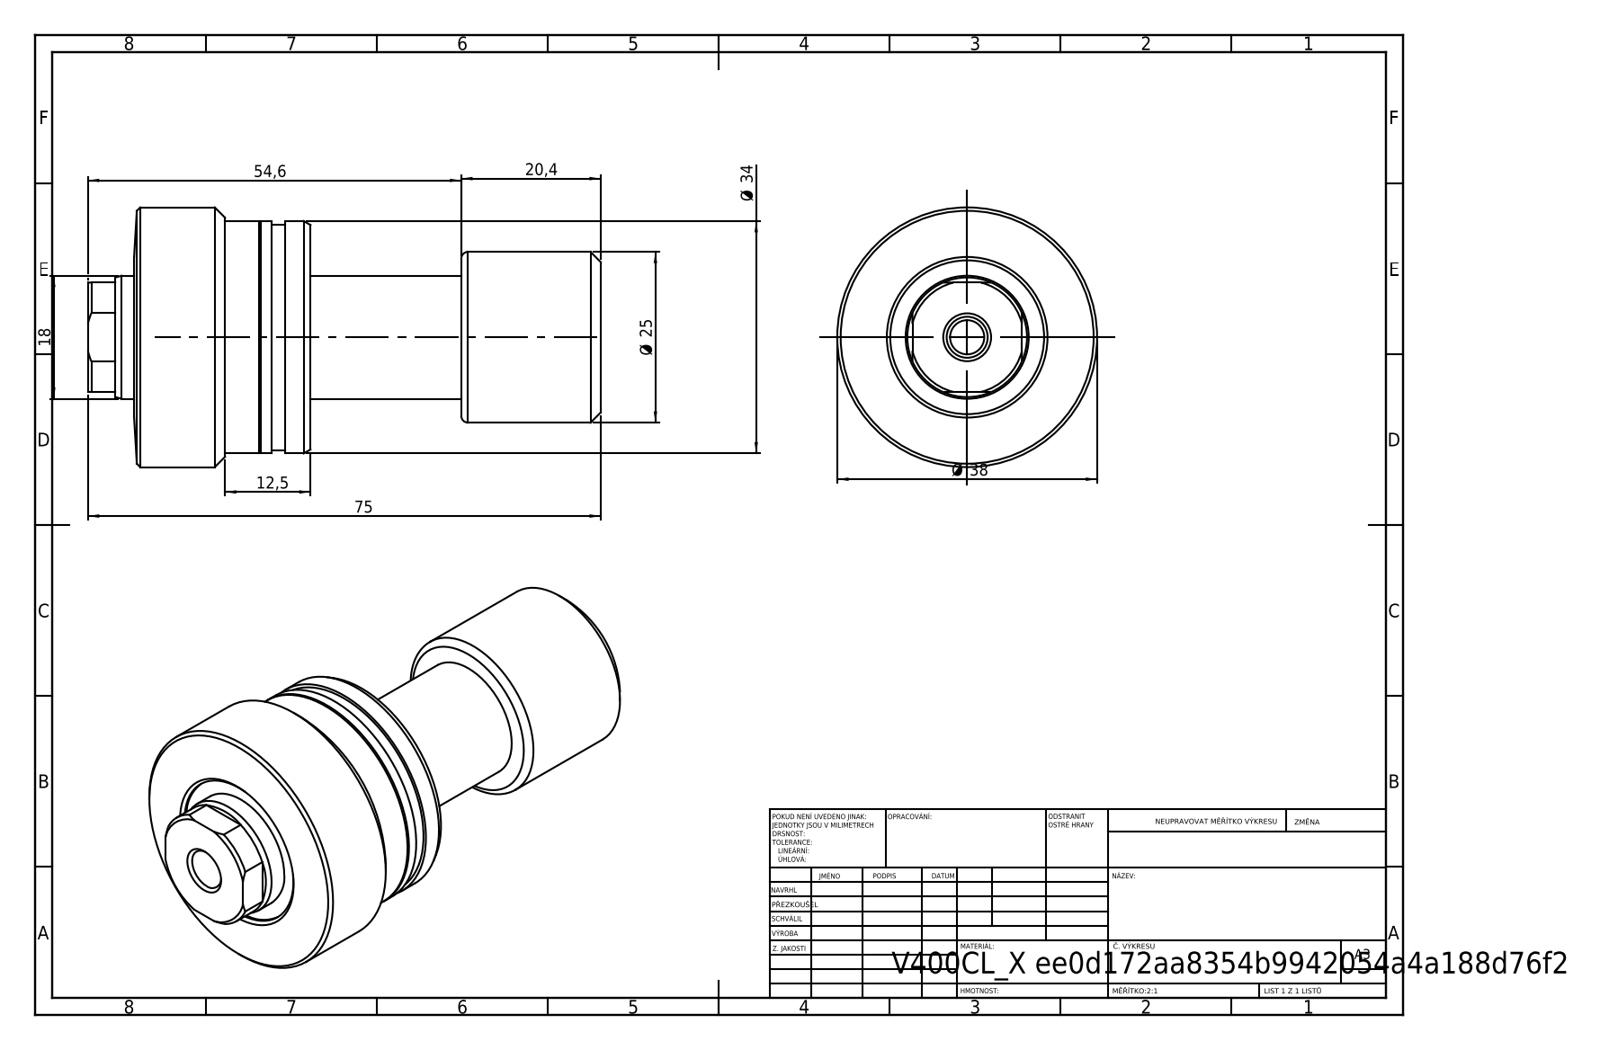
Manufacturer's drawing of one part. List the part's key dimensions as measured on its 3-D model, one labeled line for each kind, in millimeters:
Part name (STEP PRODUCT): V400CL_VC_X; V400CL_PC_X
STEP written by: SolidWorks 2019 (CONFIG_CONTROL_DESIGN)
Units: millimetres
Bodies: 2 solids, 79 faces (19 planar, 30 cylindrical, 30 other)
Overall size (bounding box): 75 × 38 × 38
Volume: 42 365 mm³ · Surface area: 12 006 mm²
Round holes (diameter × count): ⌀2.05 ×1, ⌀5 ×1, ⌀6 ×1, ⌀18 ×1, ⌀22.5 ×1
Round bosses / shafts (diameter × count): ⌀38 ×1, ⌀34 ×1, ⌀33 ×1, ⌀25 ×1
Partial cylindrical surfaces — rounded edges, fillets, slot ends (radius × count): R8.75 ×1
Main face-to-face distances: 42.45, 75, 32.55, 20.4, 22.05, 54.6, 67.45, 47.05, 25, 7.55
